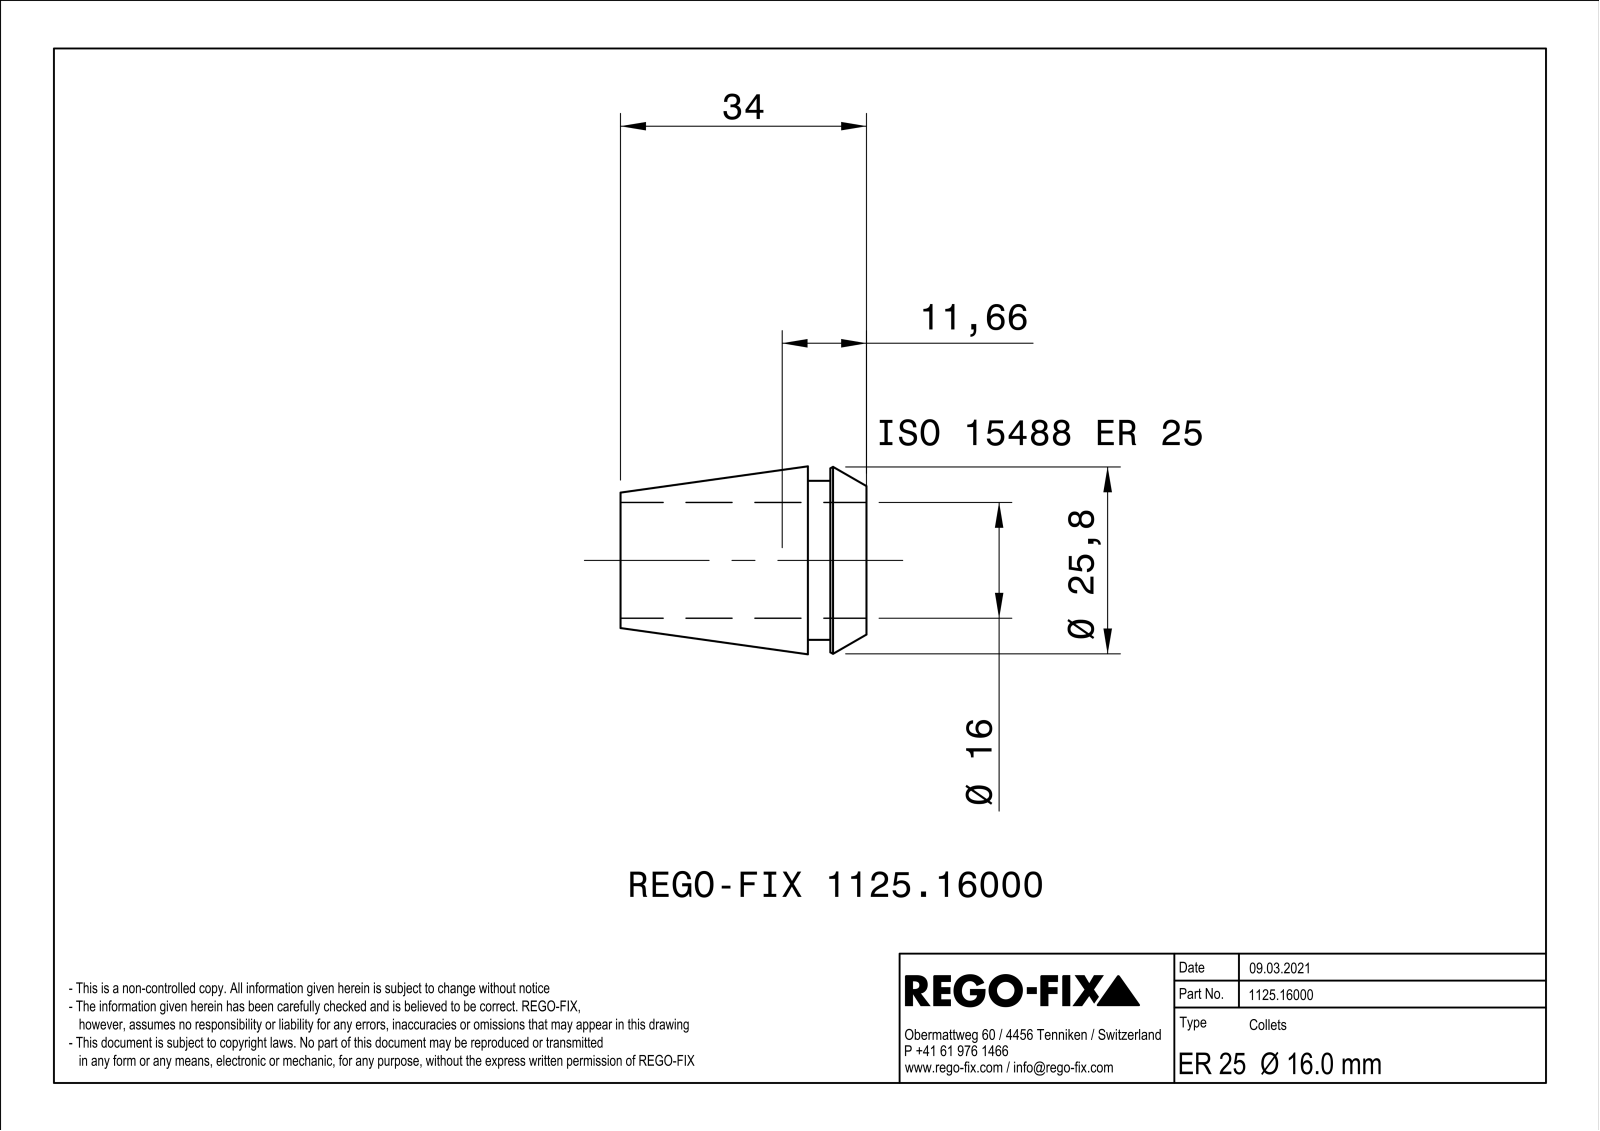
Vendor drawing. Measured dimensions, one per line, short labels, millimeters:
name: NOCUT
written by: SIEMENS PLM Software Solid Edge ST10 (AUTOMOTIVE_DESIGN)
unit: mm
bodies: 1 solid, 177 faces (72 planar, 25 cylindrical, 80 other)
size: 34 × 25.99 × 25.99
volume: 5 509 mm³; area: 6 965 mm²
holes: 1× ⌀16
bosses: 1× ⌀22
rounds: 8× R0.4
face distances: 0.8, 3.1, 5, 8.1, 34, 29, 25.9
